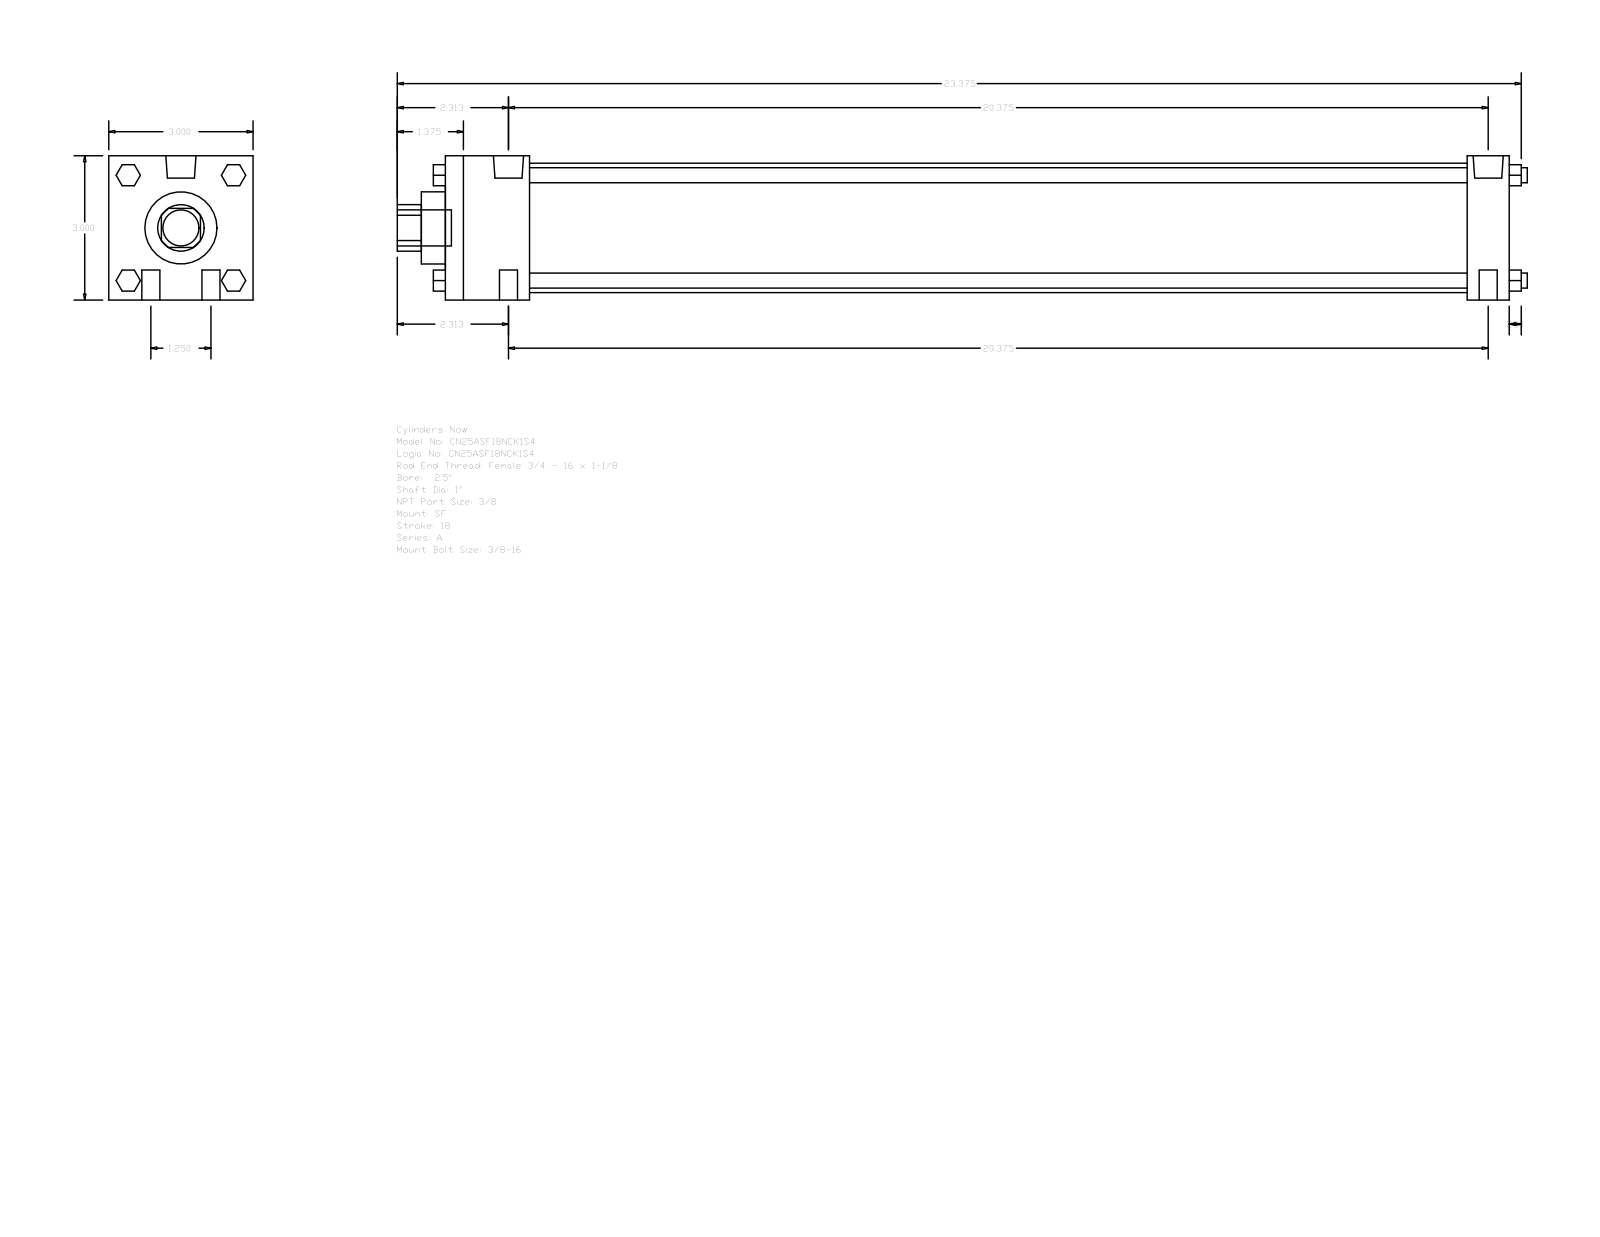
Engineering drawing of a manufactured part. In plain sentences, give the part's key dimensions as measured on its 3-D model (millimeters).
The part is named "A_SF__0250_1". Its 3-D file was written by "GSSL Pune (CONFIG_CONTROL_DESIGN)". It is 0 solids with 124 faces: 94 planar, 30 cylindrical and 0 other. Overall it measures 596.9 by 76.2 by 76.2 millimeters. Round holes: 1 of diameter 25.4, 1 of diameter 38.1, 1 of diameter 68.33. Round bosses or shafts: 4 of diameter 9.53, 4 of diameter 7.94, 2 of diameter 15.93, 2 of diameter 5.56, 1 of diameter 19.05. Partial cylindrical surfaces (rounded edges, fillets, slot ends): 1 of radius 12.29. The main face-to-face distances are 76.2, 561.98, 539.75, 22.23, 44.45, 495.3, 517.53, 12.7, 574.68, 6.35.
